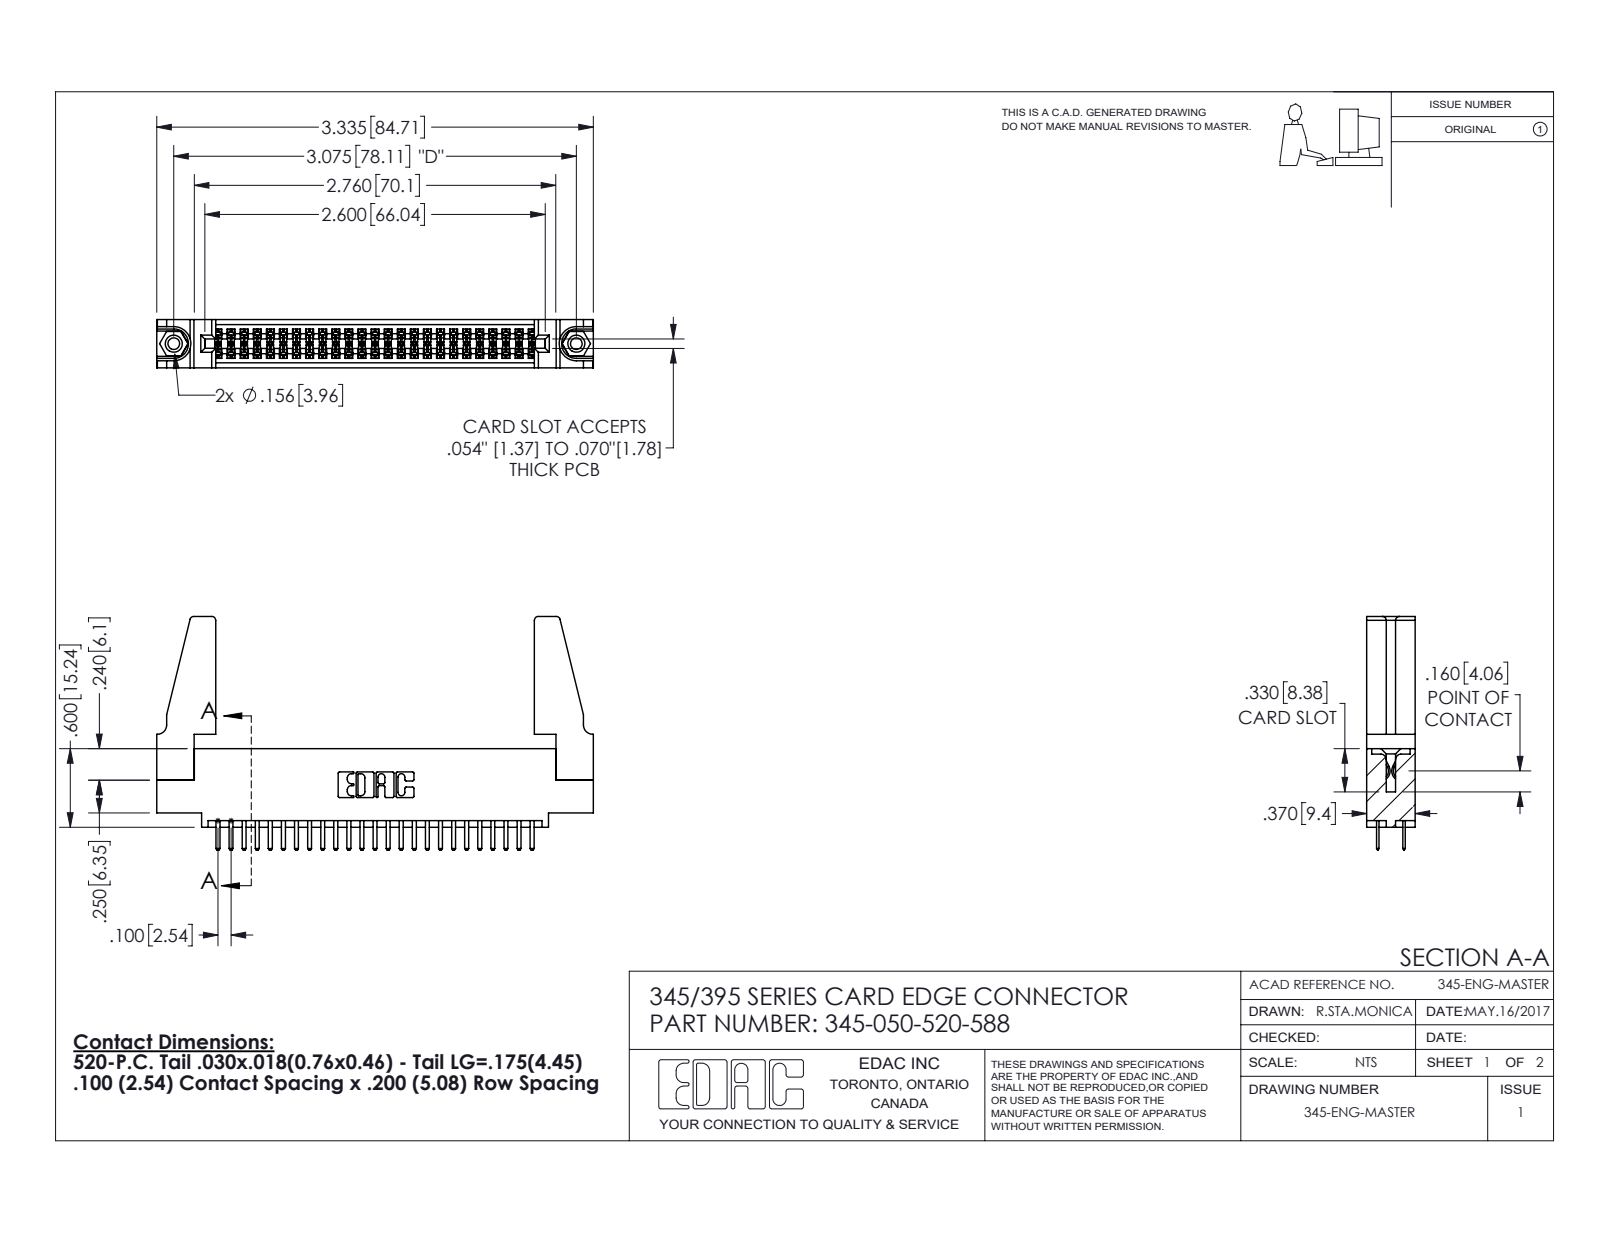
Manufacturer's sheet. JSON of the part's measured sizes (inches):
{"part_name": "345 Part_0.110 Offset - 0.156 Dia-TH; 345-050-520-588; 345-220-078_345-220-088; 345-250-001_345-250-001-102 (+1 more)", "step_written_by": "SolidWorks 2016 (CONFIG_CONTROL_DESIGN)", "units": "inches", "bodies": {"solids": 55, "faces": 2954, "planar": 1906, "cylindrical": 1032, "other": 16}, "overall_size": [3.336, 1.785, 0.37], "volume_in3": 0.685, "surface_area_in2": 22.68, "round_holes": [[0.089, 2], [0.125, 2], [0.156, 2], [0.064, 1]], "round_bosses_or_shafts": [[0.155, 2]], "partial_cylinders_radius": [[0.006, 75], [0.01, 54], [0.01, 22], [0.03, 8], [0.007, 6], [0.031, 6], [0.026, 3], [0.014, 2]], "face_to_face_distances": [0.072, 0.37, 0.298, 0.2, 0.098, 0.272, 0.025, 0.225, 0.022, 0.072], "hole_center_spacings": [0.27, 2.84, 3.075]}
